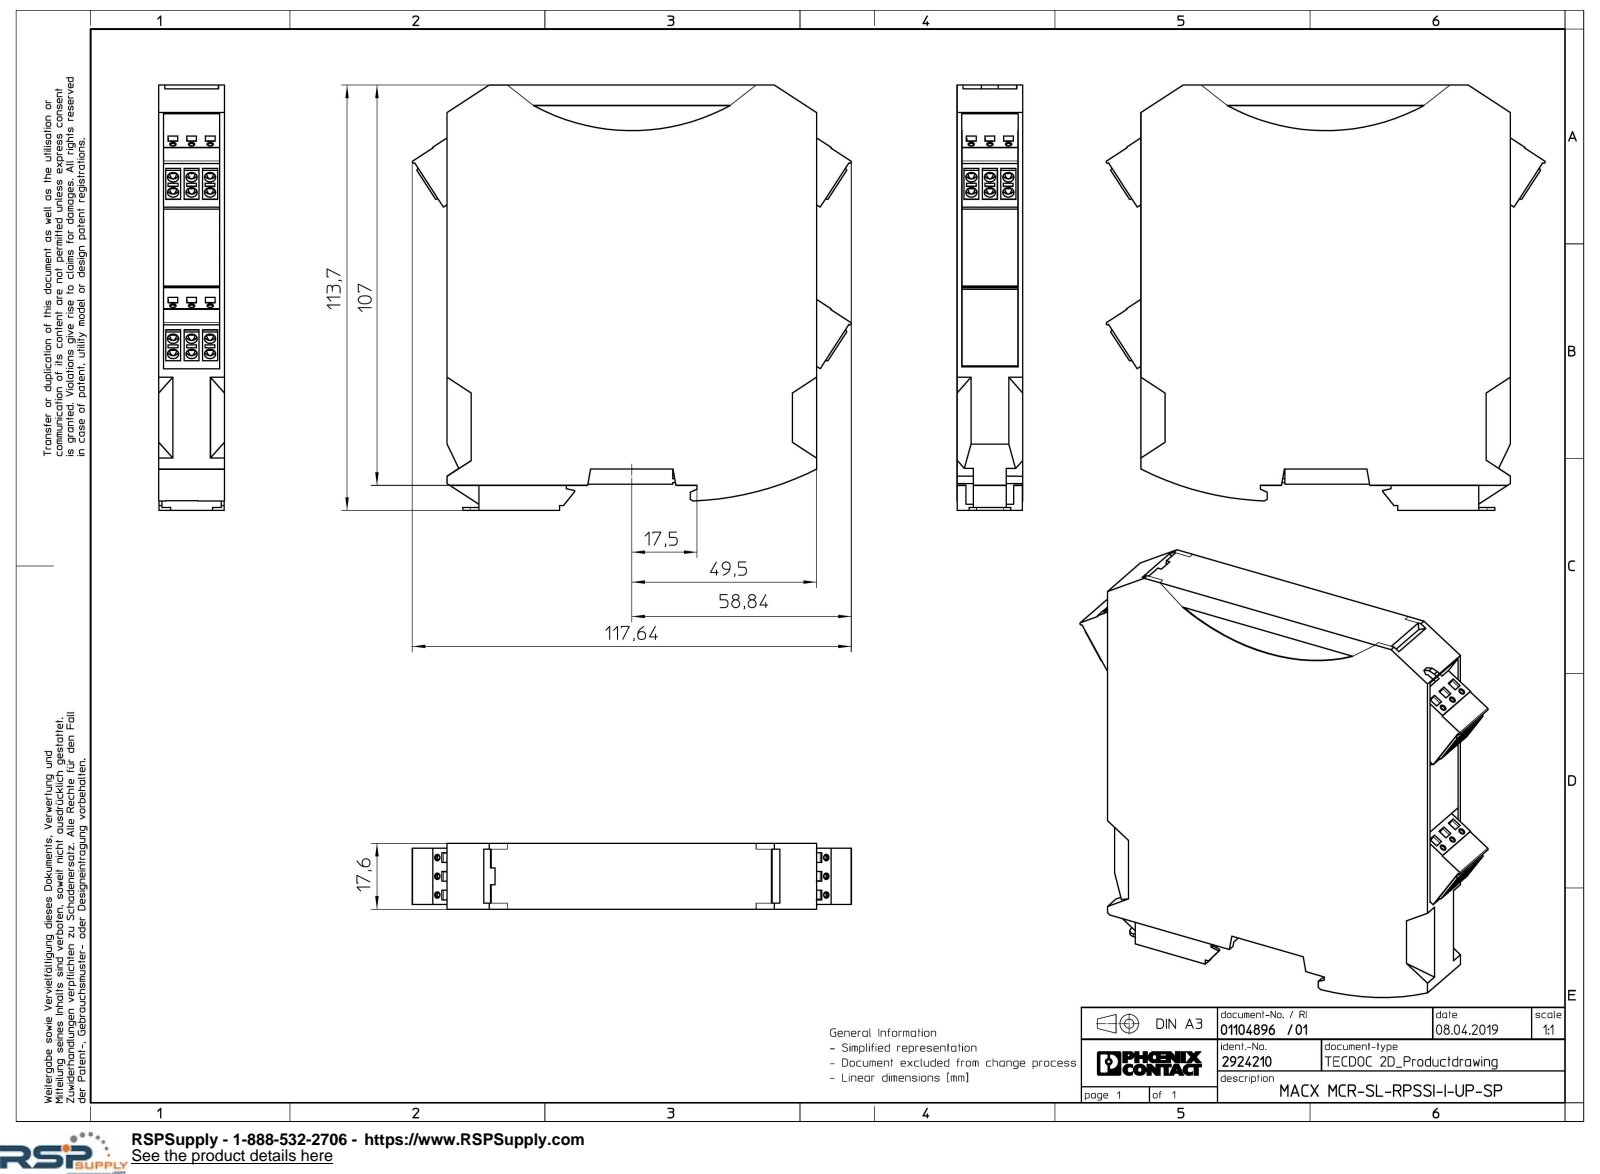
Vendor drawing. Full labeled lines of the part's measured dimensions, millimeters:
Part name (STEP PRODUCT): TVFKC_1.5_3-GY7035-select.1; TVFKC_1.5_3-BU_GY-select; ME_MAX_B-17.5_GY7042-select.2; ME_MAX_TBUS_BS_GY7042-select (+2 more)
STEP written by: Creo Elements/Direct Modeling 20.1A 29-Sep-2018 (C) Parametric Technology GmbH (AUTOMOTIVE_DESIGN)
Units: millimetres
Bodies: 8 solids, 1210 faces (946 planar, 192 cylindrical, 72 other)
Overall size (bounding box): 117.65 × 113.7 × 17.6
Volume: 180 641 mm³ · Surface area: 47 999 mm²
Round holes (diameter × count): ⌀3 ×27, ⌀1.3 ×9, ⌀1.53 ×9
Round bosses / shafts (diameter × count): ⌀2.8 ×10
Partial cylindrical surfaces — rounded edges, fillets, slot ends (radius × count): R1.25 ×18, R3 ×18, R2.9 ×9, R1.4 ×5, R0.35 ×3, R1.5 ×3, R2.5 ×3, R2 ×2
Main face-to-face distances: 17.6, 1.25, 16.3, 16.35, 15.05, 1.3, 15.1, 18.12, 15, 8.15
Hole centre spacings: 4.95, 5, 6.93, 1.23, 36.2, 36.54, 3.62, 4.84
